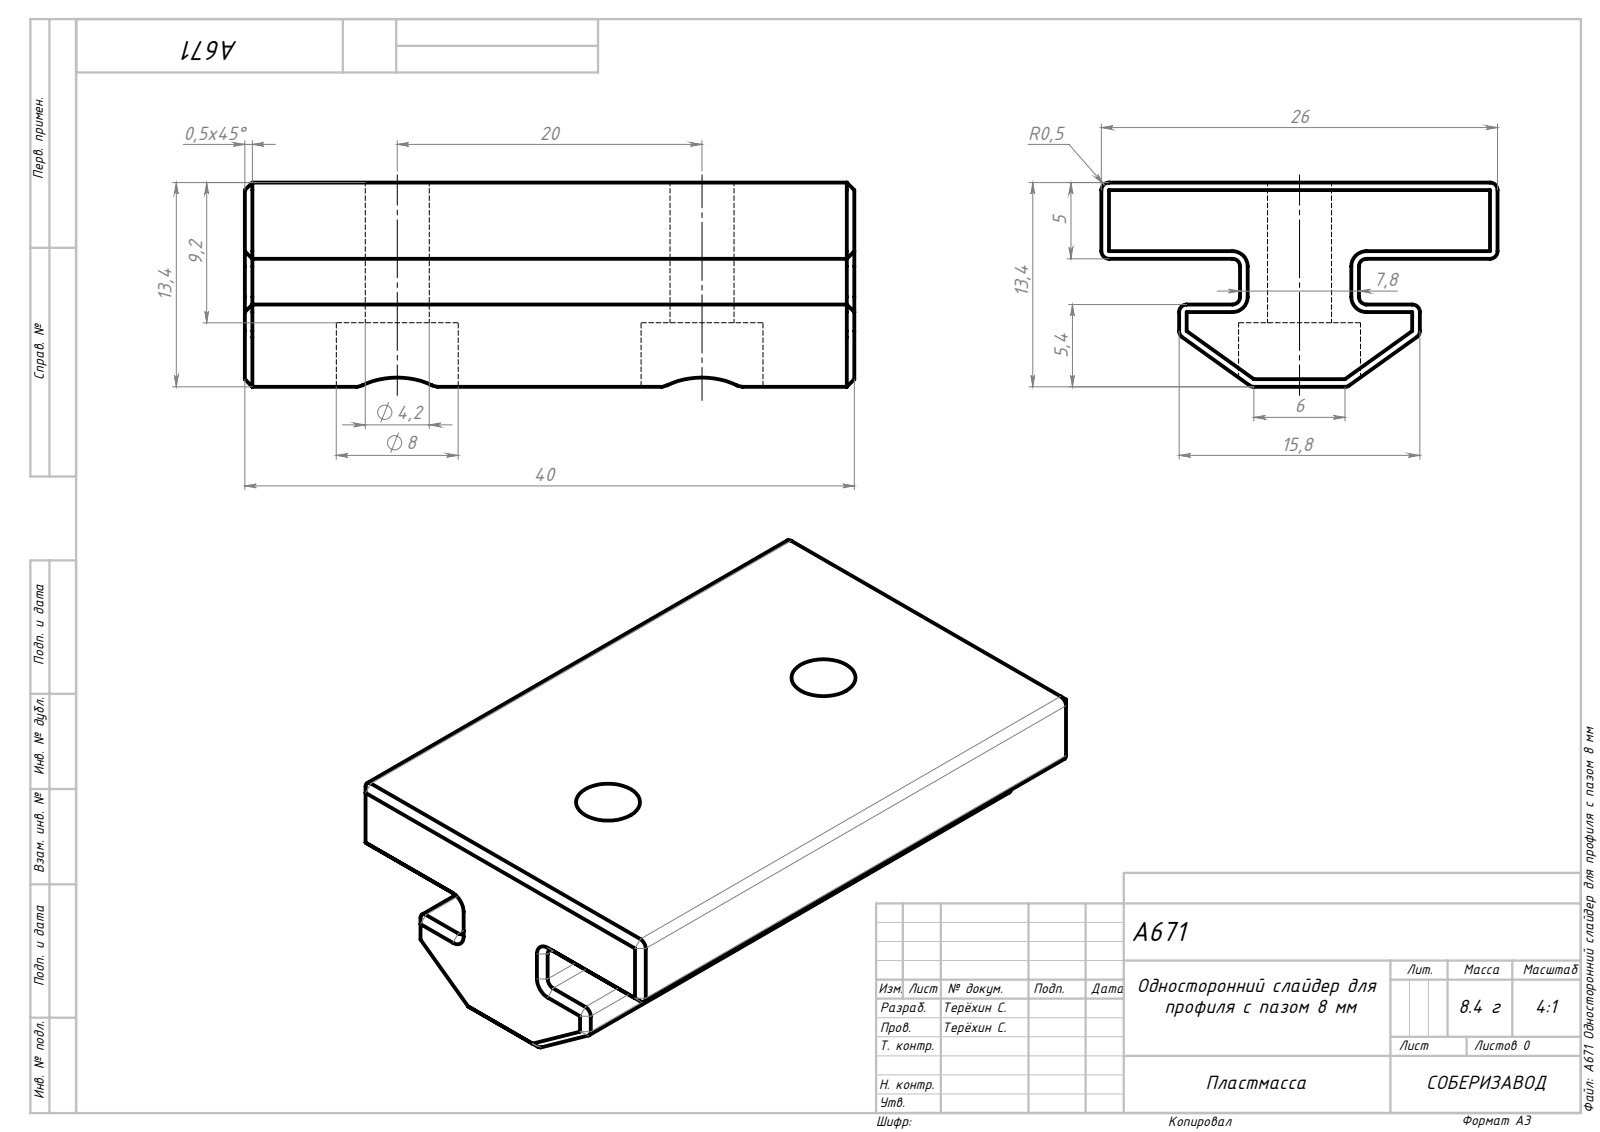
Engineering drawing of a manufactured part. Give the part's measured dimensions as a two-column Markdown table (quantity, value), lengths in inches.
| quantity | value |
| --- | --- |
| part name | A671 Односторонний слайдер для профиля с пазом 8 мм |
| STEP written by | SolidWorks 2022 (AUTOMOTIVE_DESIGN) |
| units | inches |
| bodies | 1 solid, 102 faces (48 planar, 26 cylindrical, 28 other) |
| overall size | 1.575 × 1.024 × 0.528 |
| volume | 0.501 in³ |
| surface area | 6.662 in² |
| round holes (diameter × count) | 0.165 × 2, 0.315 × 2 |
| partial cylindrical surfaces (radius × count) | 0.02 × 14 |
| main face-to-face distances | 0.197, 0.118, 0.315, 1.575, 1.024, 0.358, 0.665, 0.213, 0.331, 0.528 |
| hole center spacings | 0.787 |
